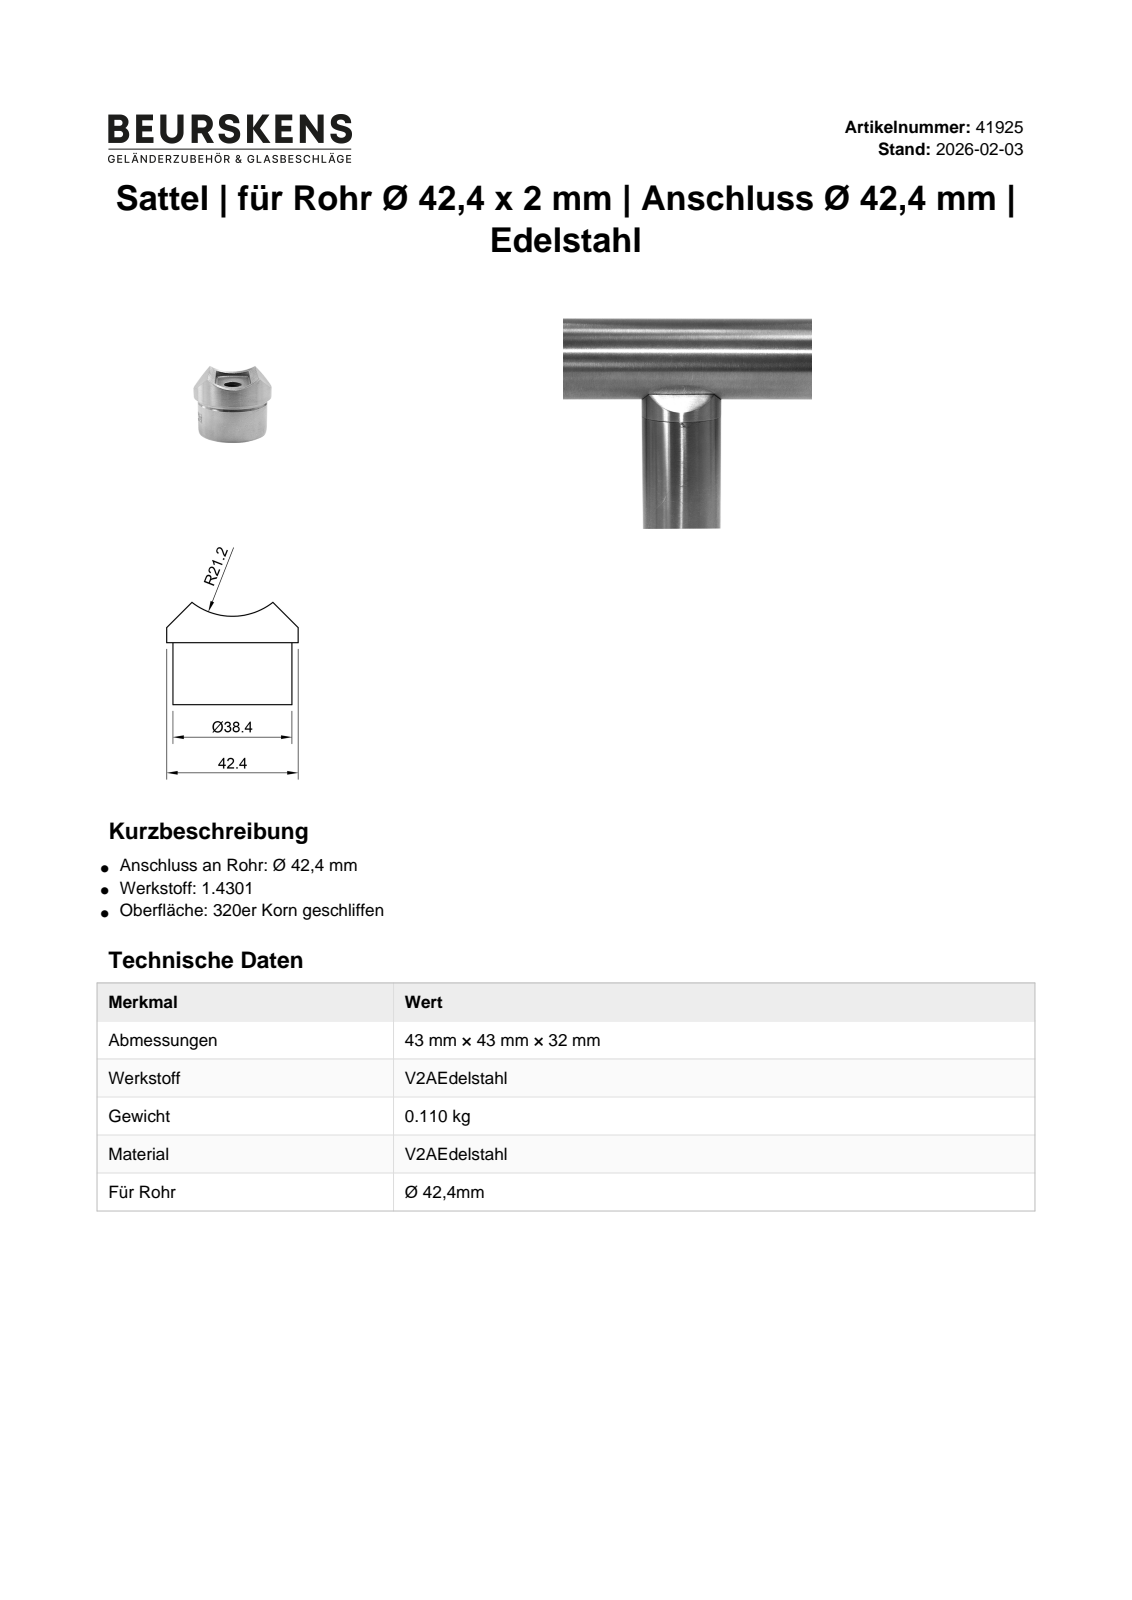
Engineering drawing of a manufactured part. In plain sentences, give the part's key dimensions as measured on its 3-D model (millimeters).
The part is named "41925". Its 3-D file was written by "Autodesk Inventor 2022 (AUTOMOTIVE_DESIGN)". It is 1 solid with 20 faces: 10 planar, 10 cylindrical and 0 other. Overall it measures 42.4 by 42.4 by 33 millimeters. Its volume is 15 015 cubic millimeters and its surface area 9 185 square millimeters. Round holes: 1 of diameter 36.4. Round bosses or shafts: 1 of diameter 42.4, 1 of diameter 38.4. Partial cylindrical surfaces (rounded edges, fillets, slot ends): 2 of radius 4.25, 1 of radius 21.2. The main face-to-face distances are 8.5, 20, 28.5, 20.12, 5.81, 14.31.
